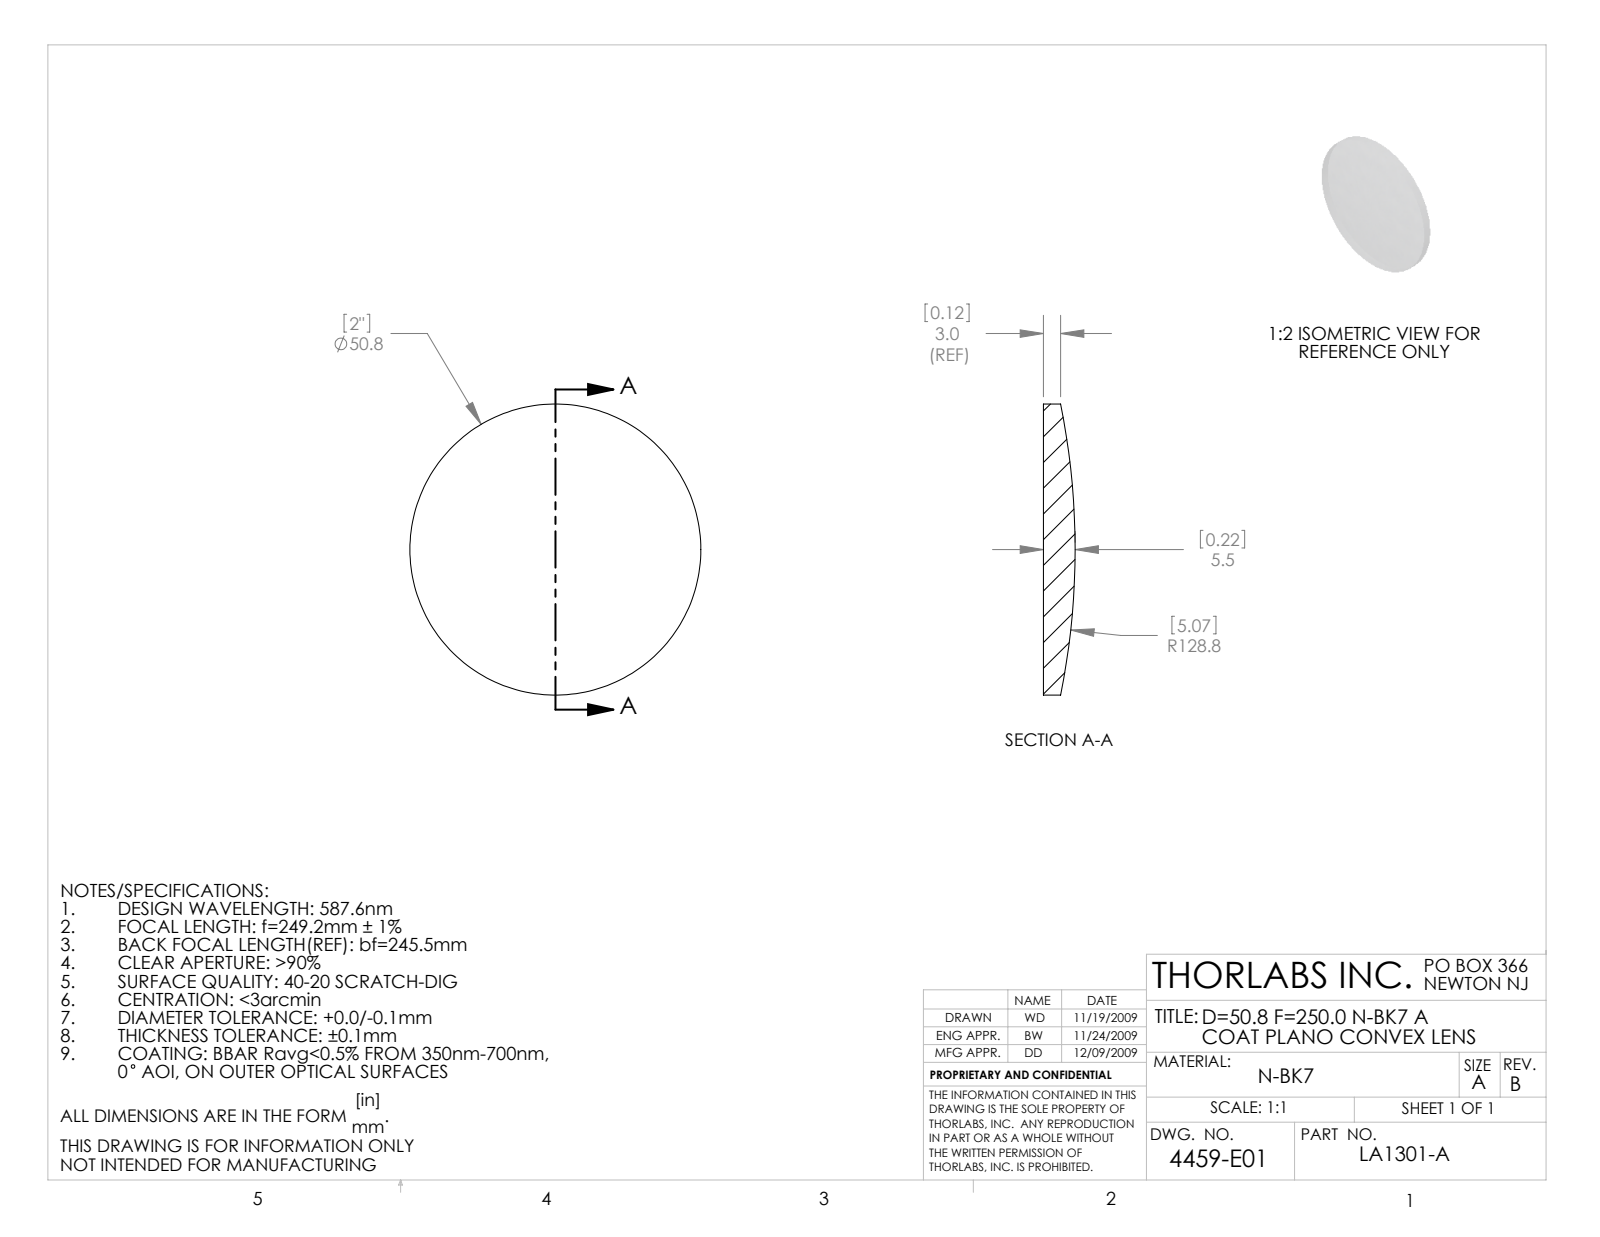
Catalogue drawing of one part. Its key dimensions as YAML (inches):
part_name: "4459-E0W"
step_written_by: "SolidWorks 2009 (AUTOMOTIVE_DESIGN)"
units: inches
bodies: {solids: 1, faces: 5, planar: 1, cylindrical: 2, other: 2}
overall_size: [2, 2, 0.217]
volume: 0.527
surface_area: 7.054
round_bosses_or_shafts:
  - {diameter: 2, count: 1}
